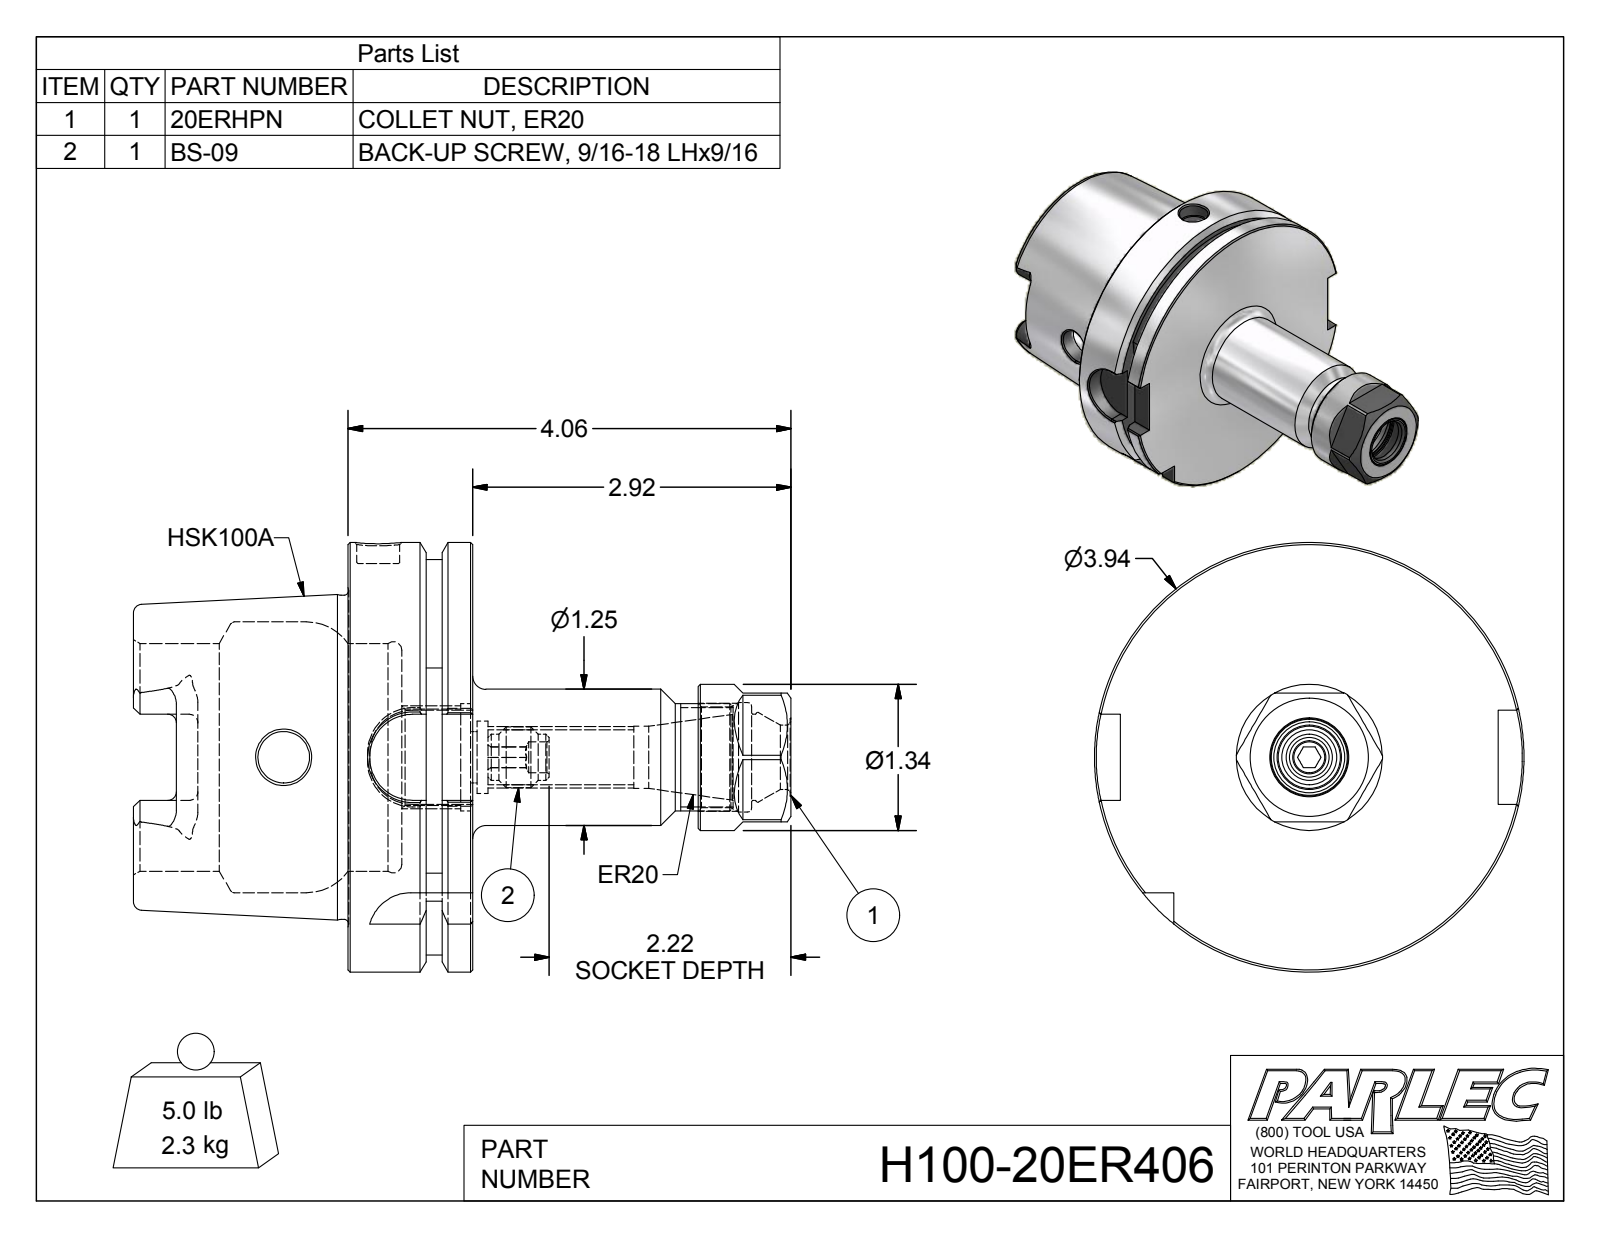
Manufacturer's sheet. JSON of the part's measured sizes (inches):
{"part_name": "H100-20ER406; H100-20ER4-1; BS-09; 20ERHPN", "step_written_by": "Autodesk Inventor 2012 (AUTOMOTIVE_DESIGN)", "units": "inches", "bodies": {"solids": 3, "faces": 189, "planar": 76, "cylindrical": 46, "other": 67}, "overall_size": [6.029, 3.937, 3.937], "volume_in3": 18.21, "surface_area_in2": 99.08, "round_holes": [[0.472, 2], [0.281, 1], [0.394, 1], [0.472, 1], [0.502, 1], [0.57, 1], [0.587, 1], [0.663, 1], [0.79, 1], [0.881, 1], [0.926, 1], [0.985, 1]], "round_bosses_or_shafts": [[3.937, 1], [2.967, 1], [1.34, 1], [1.25, 1], [0.984, 1], [0.555, 1], [0.422, 1]], "partial_cylinders_radius": [[0.079, 6], [0.192, 4], [0.394, 4], [1.811, 1]], "face_to_face_distances": [1.142, 0.492, 0.65, 1.969, 2.461, 3.11, 2.83, 0.861, 0.369, 0.28]}
